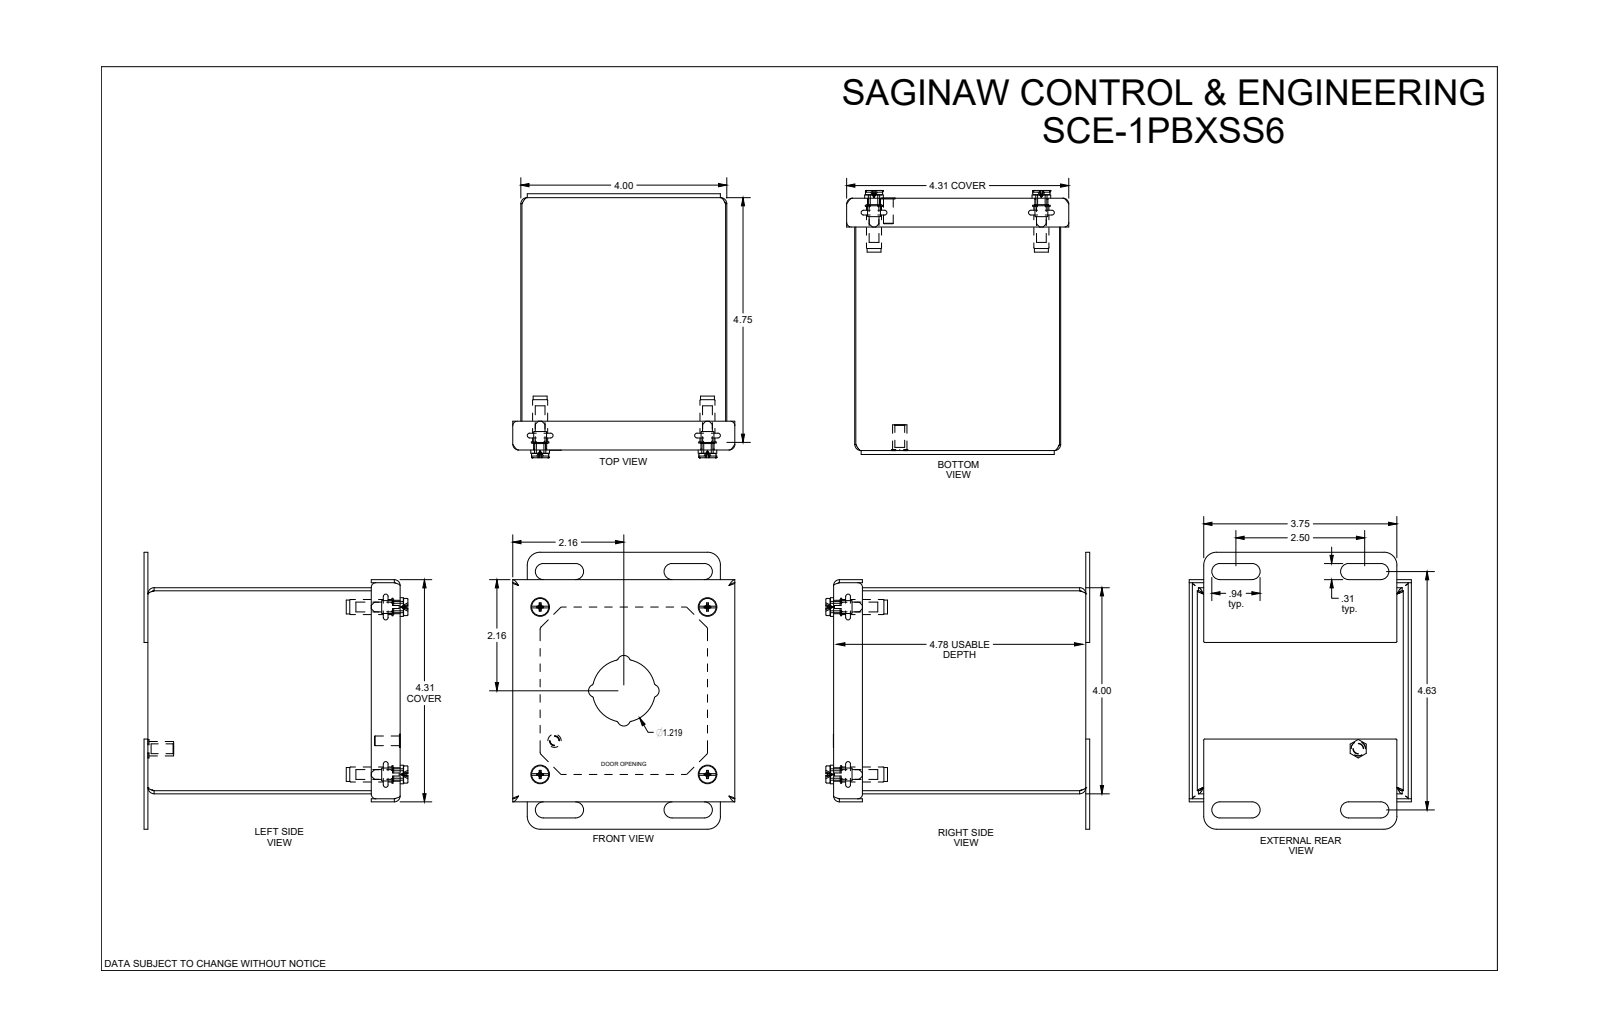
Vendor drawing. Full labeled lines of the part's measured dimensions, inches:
Part name (STEP PRODUCT): SCE-1PBX
STEP written by: SolidWorks 2021 (AUTOMOTIVE_DESIGN)
Units: inches
Bodies: 14 solids, 457 faces (163 planar, 141 cylindrical, 153 other)
Overall size (bounding box): 5.375 × 5.124 × 4.312
Volume: 8.456 in³ · Surface area: 279.7 in²
Round holes (diameter × count): ⌀0.22 ×4, ⌀0.266 ×4, ⌀0.317 ×4
Round bosses / shafts (diameter × count): ⌀0.188 ×5, ⌀0.362 ×4, ⌀0.334 ×4, ⌀0.26 ×4, ⌀0.146 ×4, ⌀0.256 ×1
Partial cylindrical surfaces — rounded edges, fillets, slot ends (radius × count): R0.06 ×20, R0.015 ×8, R0.04 ×8, R0.115 ×8, R0.156 ×8, R0.245 ×8, R0.02 ×4, R0.125 ×4
Main face-to-face distances: 0.06, 3.94, 4, 3.88, 4.838, 4.898, 4.778, 0.075, 0.135, 4.913
Hole centre spacings: 3.25, 3.25, 4.596, 3.245, 4.596, 3.245, 3.25, 4.589
